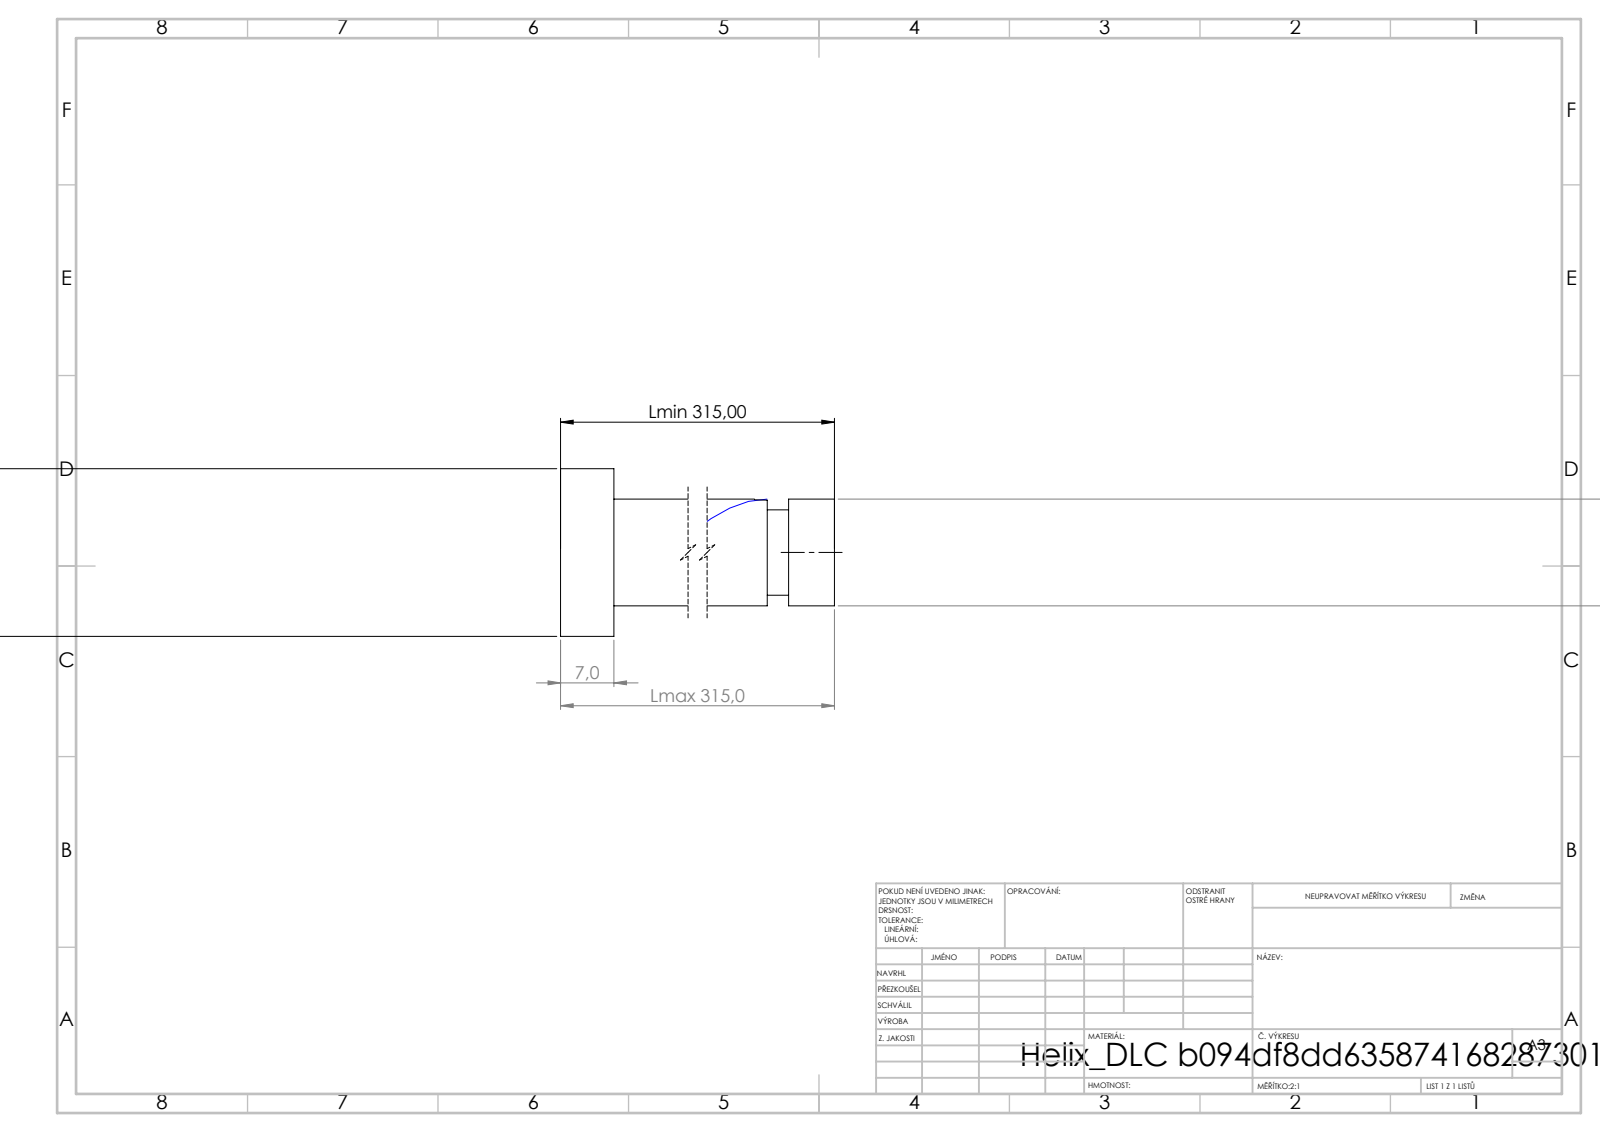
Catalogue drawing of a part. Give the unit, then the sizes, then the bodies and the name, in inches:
Units: inches
Overall size (bounding box): 12.402 × 0.866 × 0.866
Round bosses / shafts (diameter × count): ⌀0.866 ×1, ⌀0.551 ×1, ⌀0.441 ×1
Main face-to-face distances: 0.276, 12.402, 12.126, 12.165, 11.889, 0.237, 12.055, 11.779, 0.11, 0.347
Volume: 3.018 in³ · Surface area: 23.53 in²
Bodies: 1 solid, 21 faces (6 planar, 14 cylindrical, 1 other)
STEP written by: SolidWorks 2019 (CONFIG_CONTROL_DESIGN)
